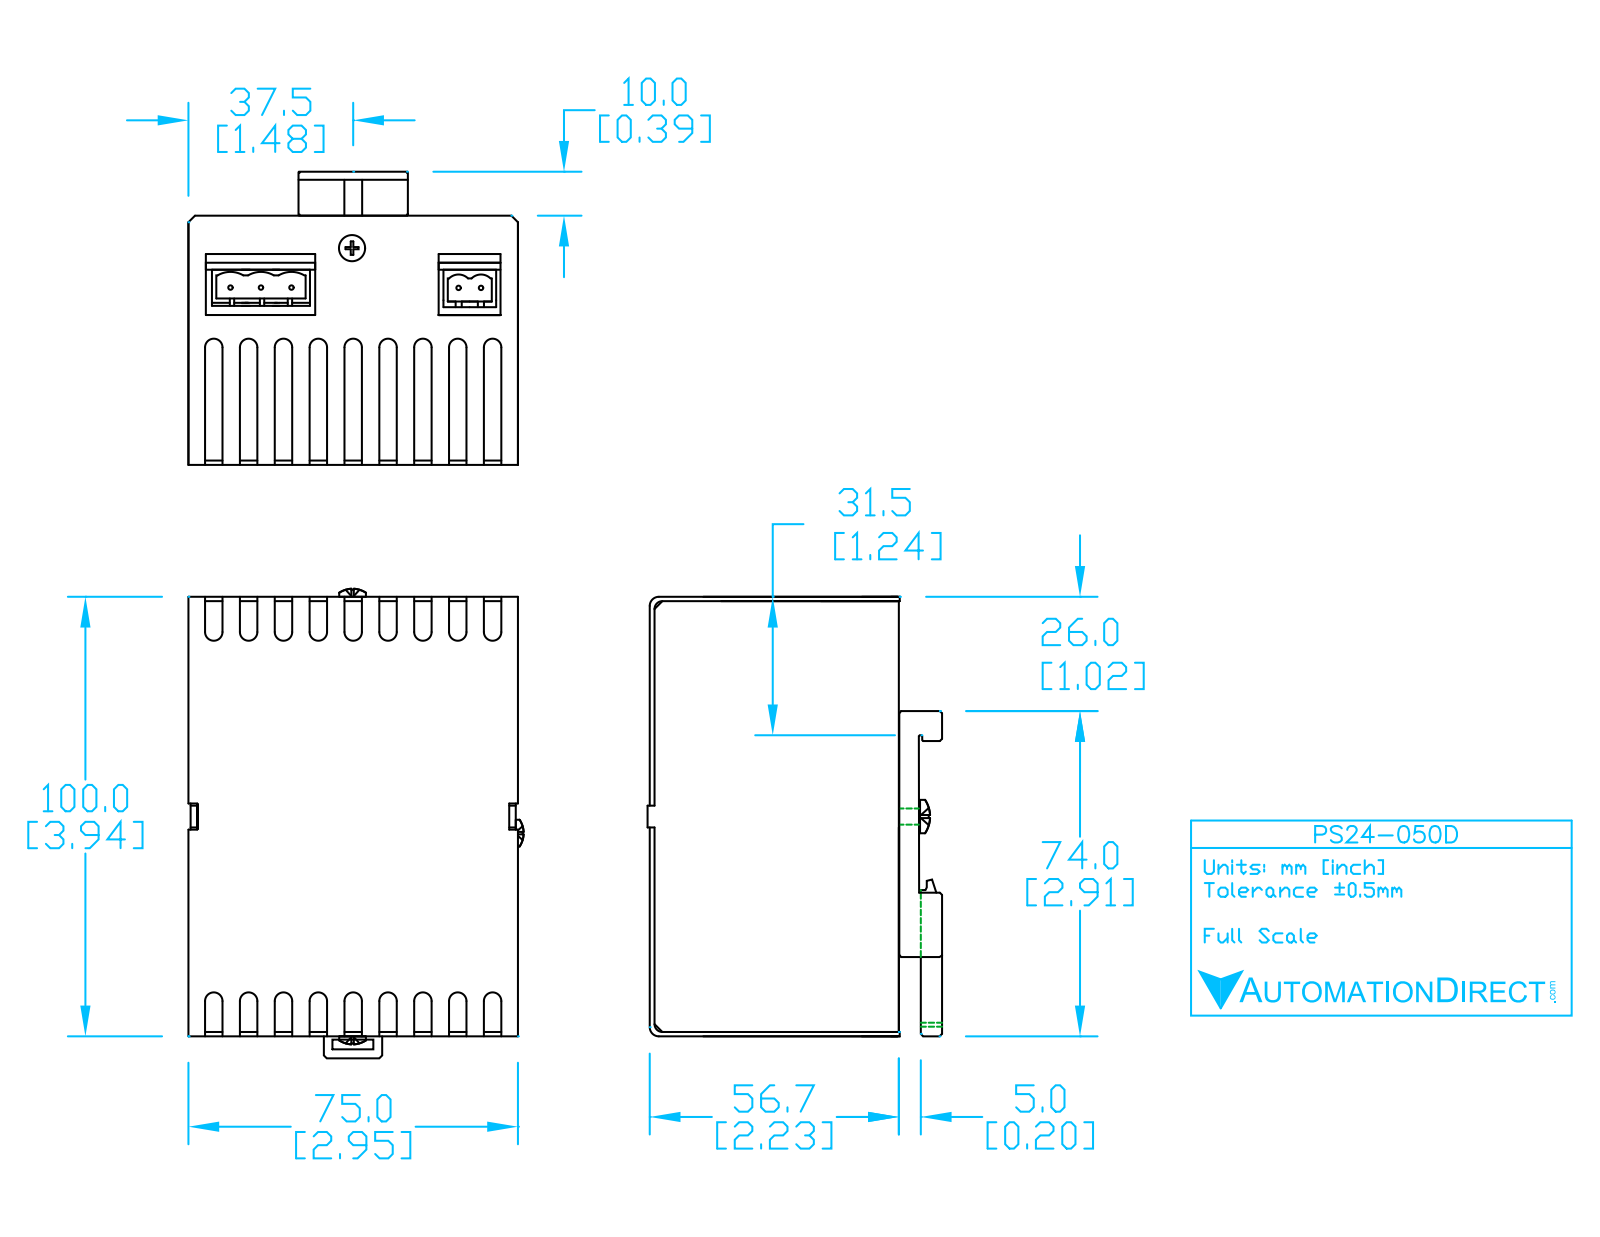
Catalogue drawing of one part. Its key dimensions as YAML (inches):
part_name: "PS24-050D"
step_written_by: "SolidWorks 2011 (CONFIG_CONTROL_DESIGN)"
units: inches
bodies: {solids: 1, faces: 610, planar: 394, cylindrical: 144, other: 72}
overall_size: [4.545, 3.036, 2.694]
volume: 18.35
surface_area: 93.58
round_holes:
  - {diameter: 0.15, count: 5}
  - {diameter: 0.135, count: 1}
round_bosses_or_shafts:
  - {diameter: 0.3, count: 1}
  - {diameter: 0.265, count: 1}
  - {diameter: 0.212, count: 1}
  - {diameter: 0.21, count: 1}
partial_cylinders:
  - {radius: 0.076, count: 45}
  - {radius: 0.06, count: 6}
  - {radius: 0.015, count: 2}
  - {radius: 0.02, count: 2}
face_to_face_distances: [0.04, 2.948, 3.9, 2.495, 0.039, 2.909, 2.23, 0.68, 3.175, 0.725]
hole_center_spacings: [0.2, 0.312, 0.313, 0.625, 1.064, 1.067, 1.485, 1.685]
